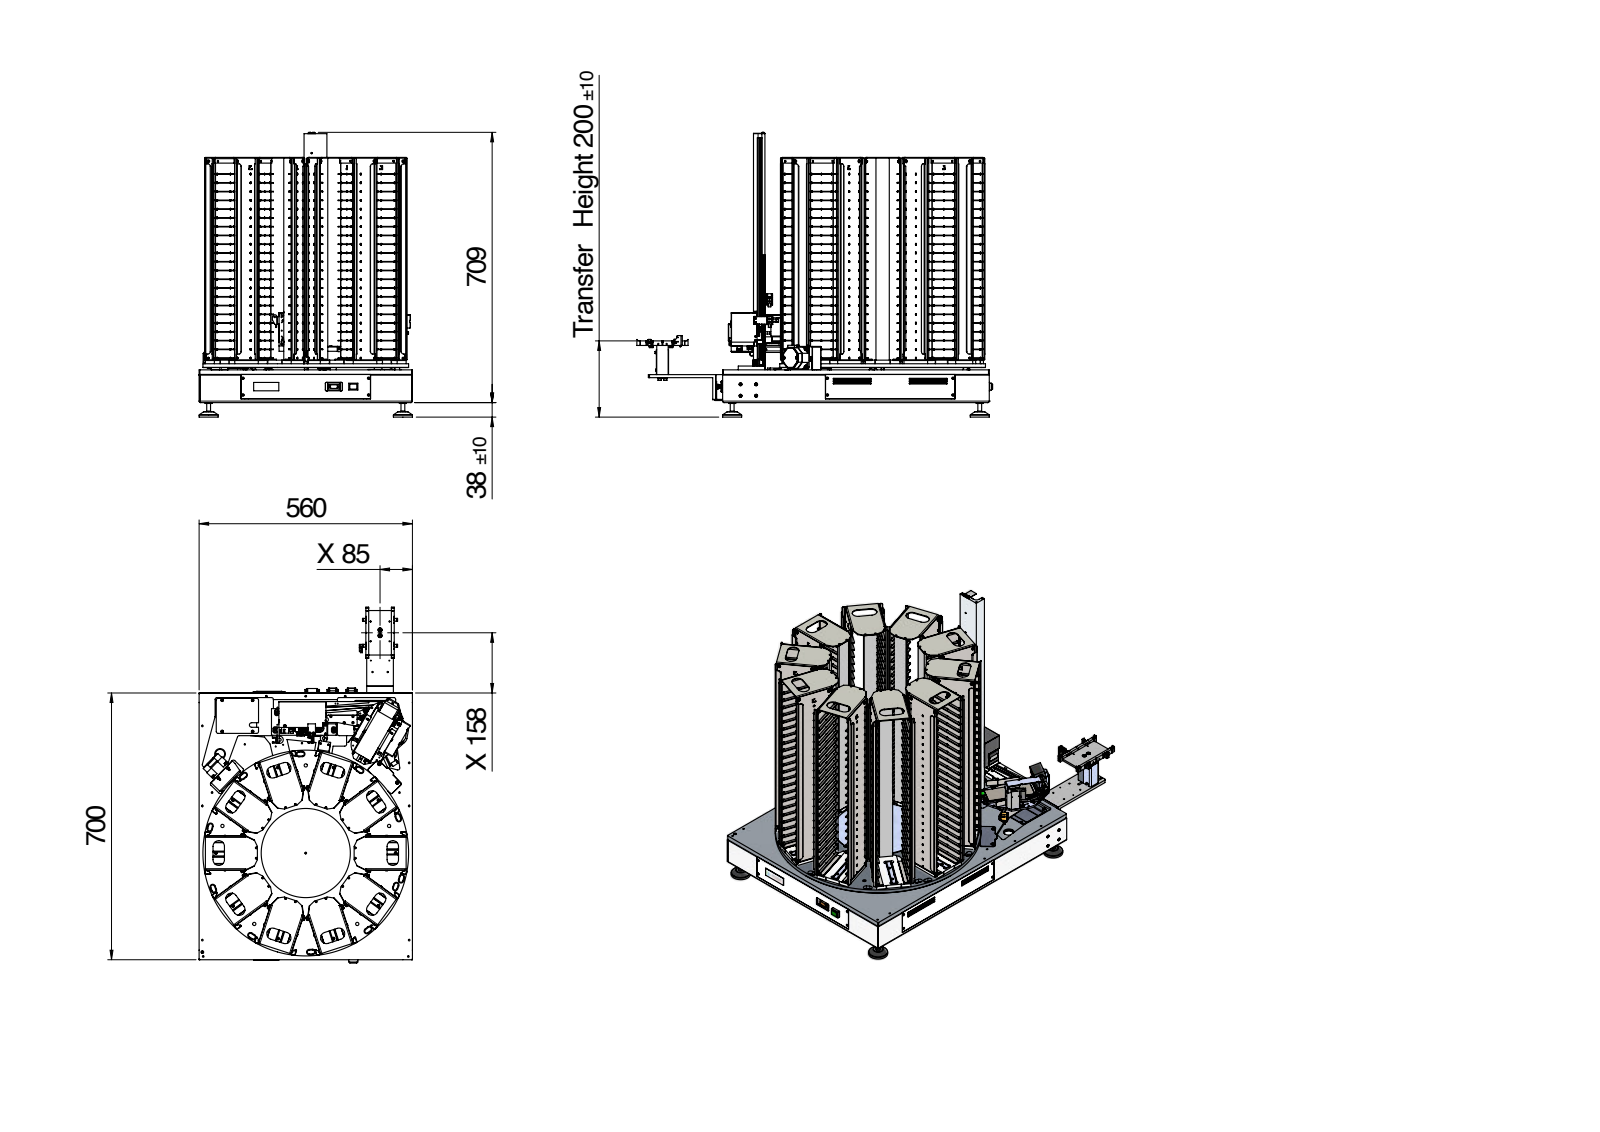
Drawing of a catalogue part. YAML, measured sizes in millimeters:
part_name: "9341000"
step_written_by: "SolidWorks 2022 (AUTOMOTIVE_DESIGN)"
units: millimeters
bodies: {solids: 37, faces: 7110, planar: 3914, cylindrical: 3076, other: 120}
overall_size: [933.98, 743.8, 560.01]
volume: 8838000
surface_area: 3304000
round_holes:
  - {diameter: 2.5, count: 61}
  - {diameter: 4.2, count: 55}
  - {diameter: 3.3, count: 33}
  - {diameter: 4, count: 22}
  - {diameter: 6.5, count: 21}
  - {diameter: 7.1, count: 16}
  - {diameter: 3.4, count: 10}
  - {diameter: 6.2, count: 10}
  - {diameter: 3.1, count: 8}
  - {diameter: 8, count: 8}
  - {diameter: 11, count: 8}
  - {diameter: 5.3, count: 6}
round_bosses_or_shafts:
  - {diameter: 50.01, count: 4}
  - {diameter: 10, count: 4}
  - {diameter: 1.5, count: 3}
  - {diameter: 540, count: 1}
  - {diameter: 234, count: 1}
  - {diameter: 15.5, count: 1}
  - {diameter: 14.5, count: 1}
partial_cylinders:
  - {radius: 0.1, count: 832}
  - {radius: 0.25, count: 832}
  - {radius: 2, count: 171}
  - {radius: 5, count: 121}
  - {radius: 2.5, count: 114}
  - {radius: 1, count: 55}
  - {radius: 3, count: 36}
  - {radius: 1.5, count: 26}
face_to_face_distances: [2, 72, 74, 12, 90, 86, 84, 6, 10, 28]
hole_center_spacings: [41, 30, 50.8, 158.39, 85.72, 206.95, 270.38, 437.48]
